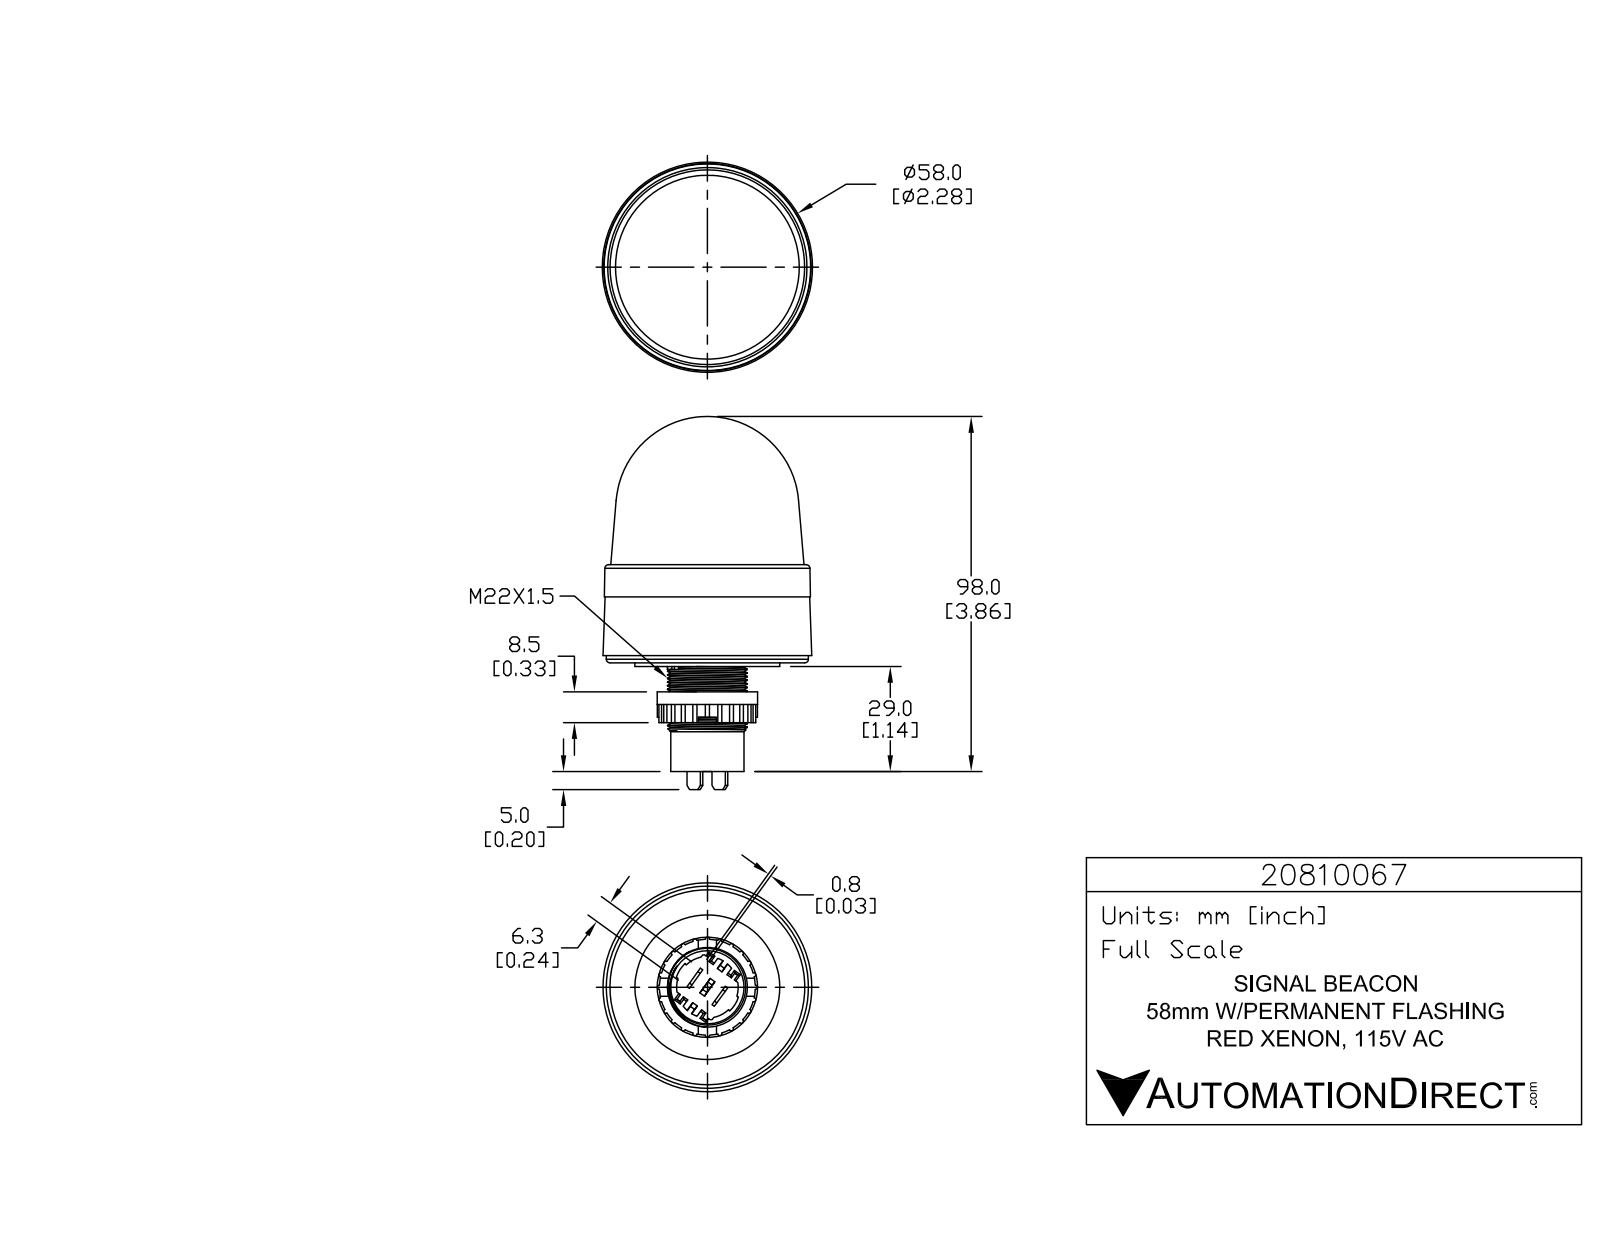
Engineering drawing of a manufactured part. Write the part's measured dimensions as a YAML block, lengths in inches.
part_name: "20810067"
step_written_by: "SolidWorks 2015 (AUTOMOTIVE_DESIGN)"
units: inches
bodies: {solids: 1, faces: 266, planar: 119, cylindrical: 120, other: 27}
overall_size: [4.051, 2.269, 2.269]
volume: 9.016
surface_area: 31.05
round_holes:
  - {diameter: 0.906, count: 1}
round_bosses_or_shafts:
  - {diameter: 2.197, count: 1}
  - {diameter: 1.575, count: 1}
  - {diameter: 1.091, count: 1}
  - {diameter: 0.866, count: 1}
  - {diameter: 0.795, count: 1}
partial_cylinders:
  - {radius: 0.023, count: 24}
  - {radius: 0.02, count: 2}
  - {radius: 0.335, count: 1}
  - {radius: 0.354, count: 1}
  - {radius: 0.522, count: 1}
face_to_face_distances: [0.039, 0.276, 0.118, 1.142, 0.335, 0.315, 1.063, 0.748, 1.024, 0.728]
